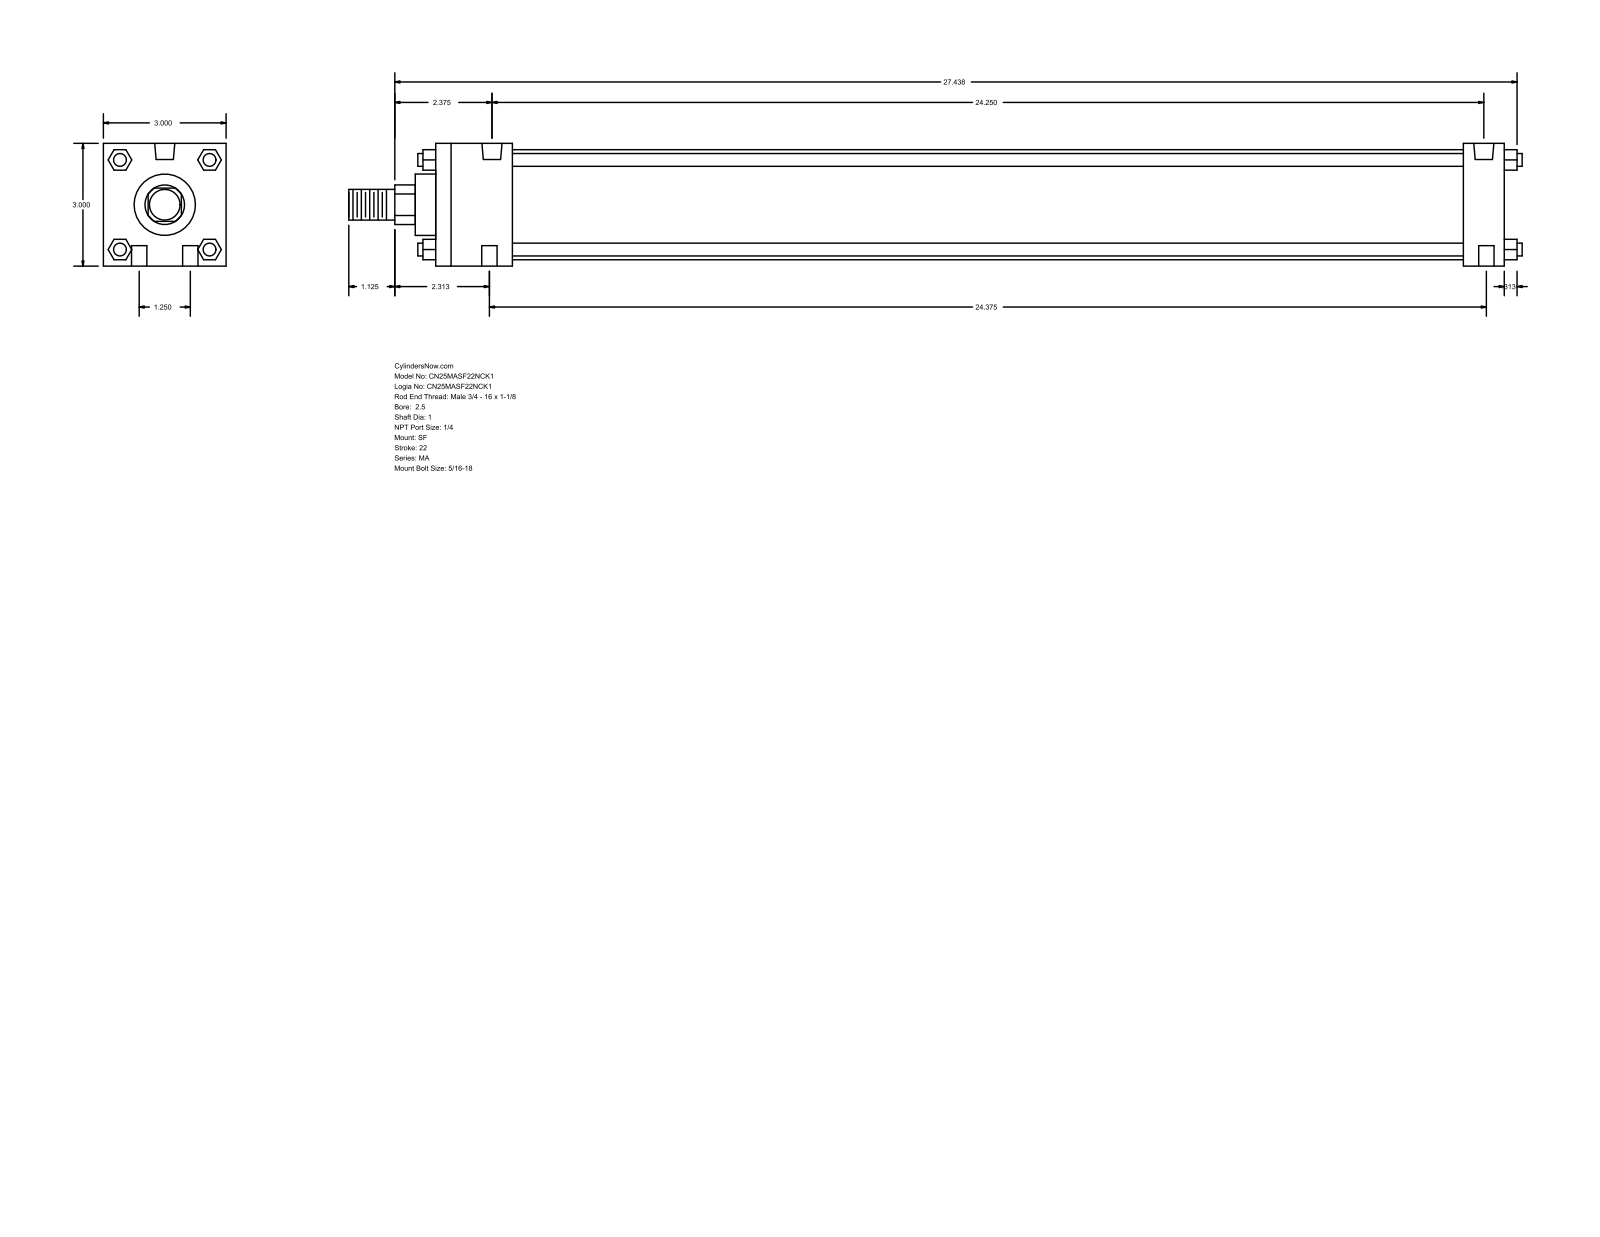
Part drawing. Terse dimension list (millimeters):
name: MA_SF__0250_1
written by: GSSL Pune (CONFIG_CONTROL_DESIGN)
unit: mm
bodies: 0 solids, 124 faces (94 planar, 30 cylindrical, 0 other)
size: 728.66 × 76.2 × 76.2
holes: 4× ⌀9.53, 2× ⌀7.94, 2× ⌀12.49
bosses: 4× ⌀7.94, 1× ⌀68.33, 1× ⌀38.1, 1× ⌀25.4, 1× ⌀19.05
rounds: 1× R12.29
face distances: 76.2, 663.58, 12.7, 25.4, 638.18, 47.63, 590.55, 615.95, 27.81, 48.17
hole spacings: 15.96, 617.73, 31.76, 615.94, 619.12, 619.93
